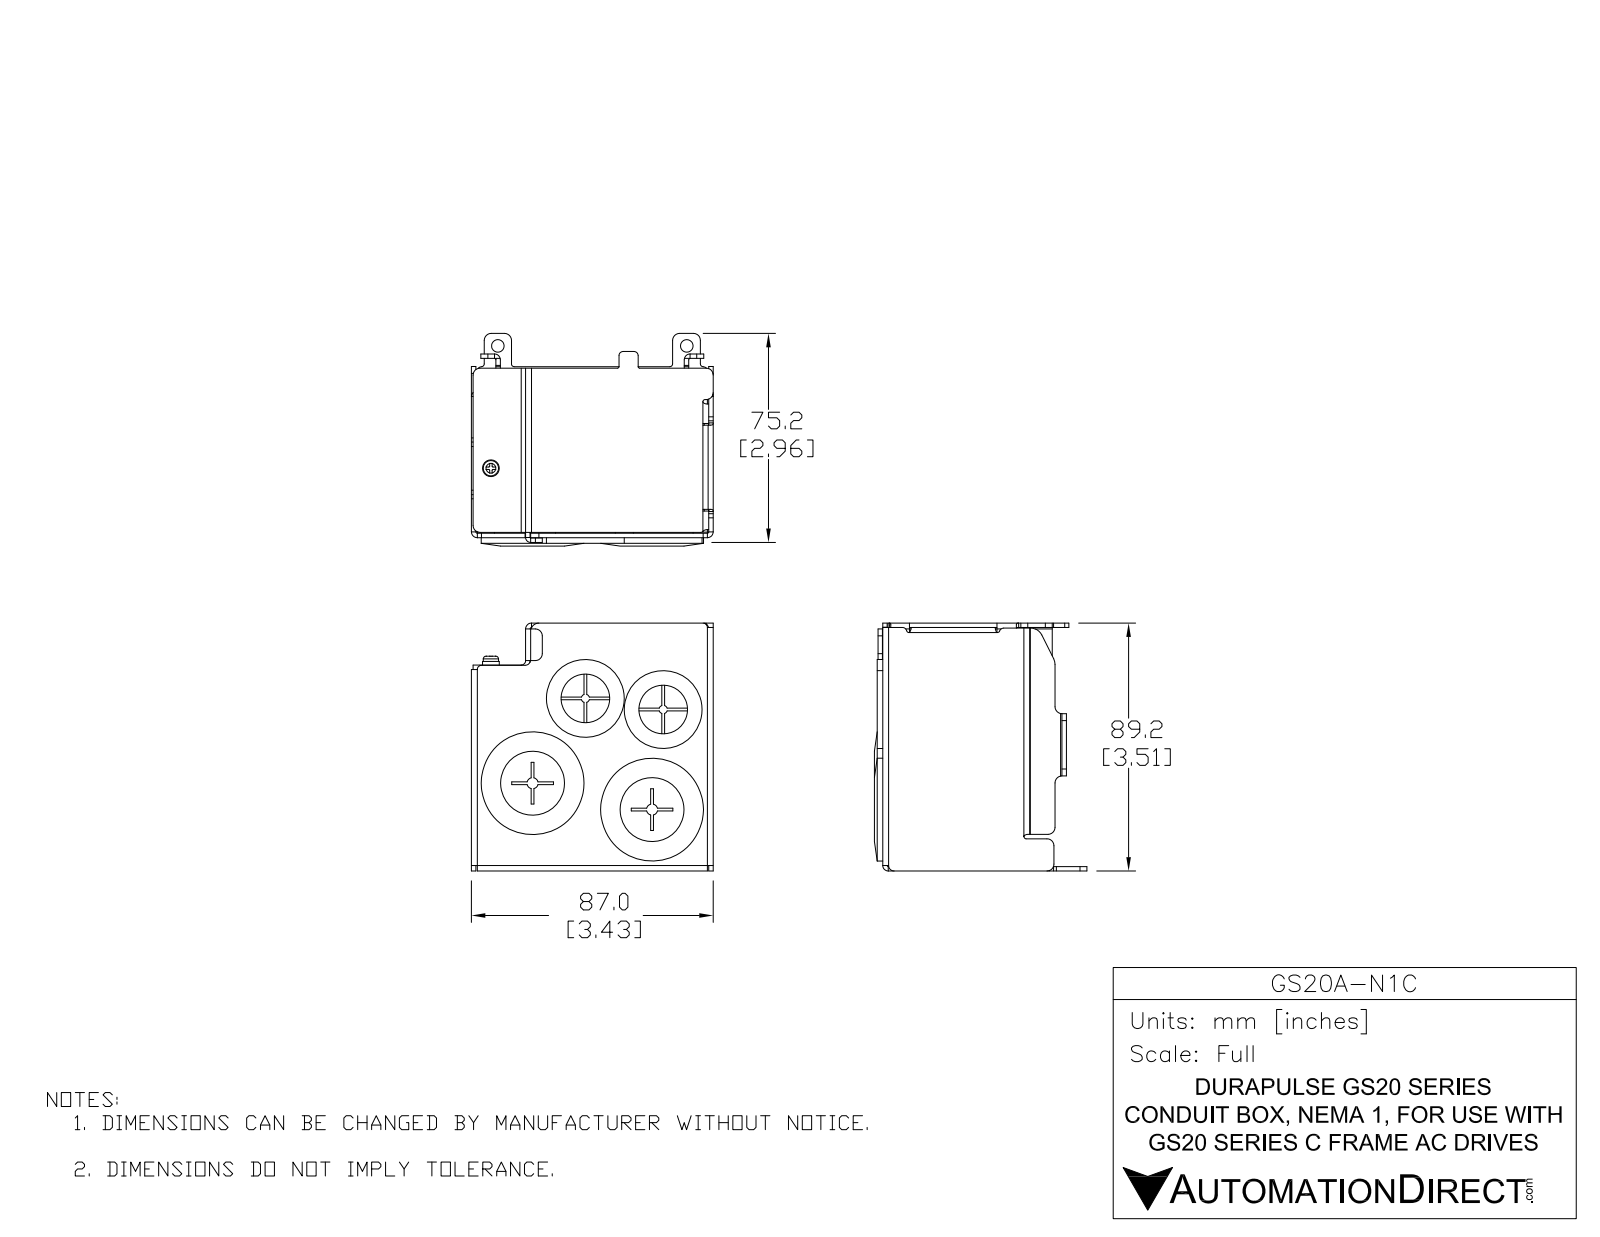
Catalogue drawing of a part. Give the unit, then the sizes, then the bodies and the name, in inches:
Units: inches
Overall size (bounding box): 3.614 × 3.425 × 3.012
Round holes (diameter × count): ⌀0.138 ×3, ⌀0.128 ×2, ⌀0.177 ×2, ⌀0.689 ×2, ⌀0.846 ×2, ⌀0.886 ×2, ⌀1.094 ×2, ⌀0.097 ×1, ⌀0.157 ×1
Round bosses / shafts (diameter × count): ⌀1.457 ×2, ⌀1.102 ×2, ⌀1.083 ×2, ⌀0.846 ×2, ⌀0.315 ×2, ⌀0.31 ×2, ⌀0.272 ×2, ⌀0.261 ×2
Partial cylindrical surfaces — rounded edges, fillets, slot ends (radius × count): R0.098 ×25, R0.059 ×12, R0.02 ×10, R0.083 ×8, R0.031 ×6, R0.008 ×5, R0.071 ×5, R0.079 ×5
Main face-to-face distances: 0.063, 3.449, 3.362, 3.386, 3.299, 3.512, 3.425, 3.016, 0.346, 0.594
Hole centre spacings: 0.74, 2.455, 1.113, 1.141, 1.415, 1.426, 1.734, 1.735
Volume: 3.437 in³ · Surface area: 111.6 in²
Bodies: 14 solids, 506 faces (243 planar, 204 cylindrical, 59 other)
Part name (STEP PRODUCT): GS20A- NIC
STEP written by: SolidWorks 2017 (CONFIG_CONTROL_DESIGN)
